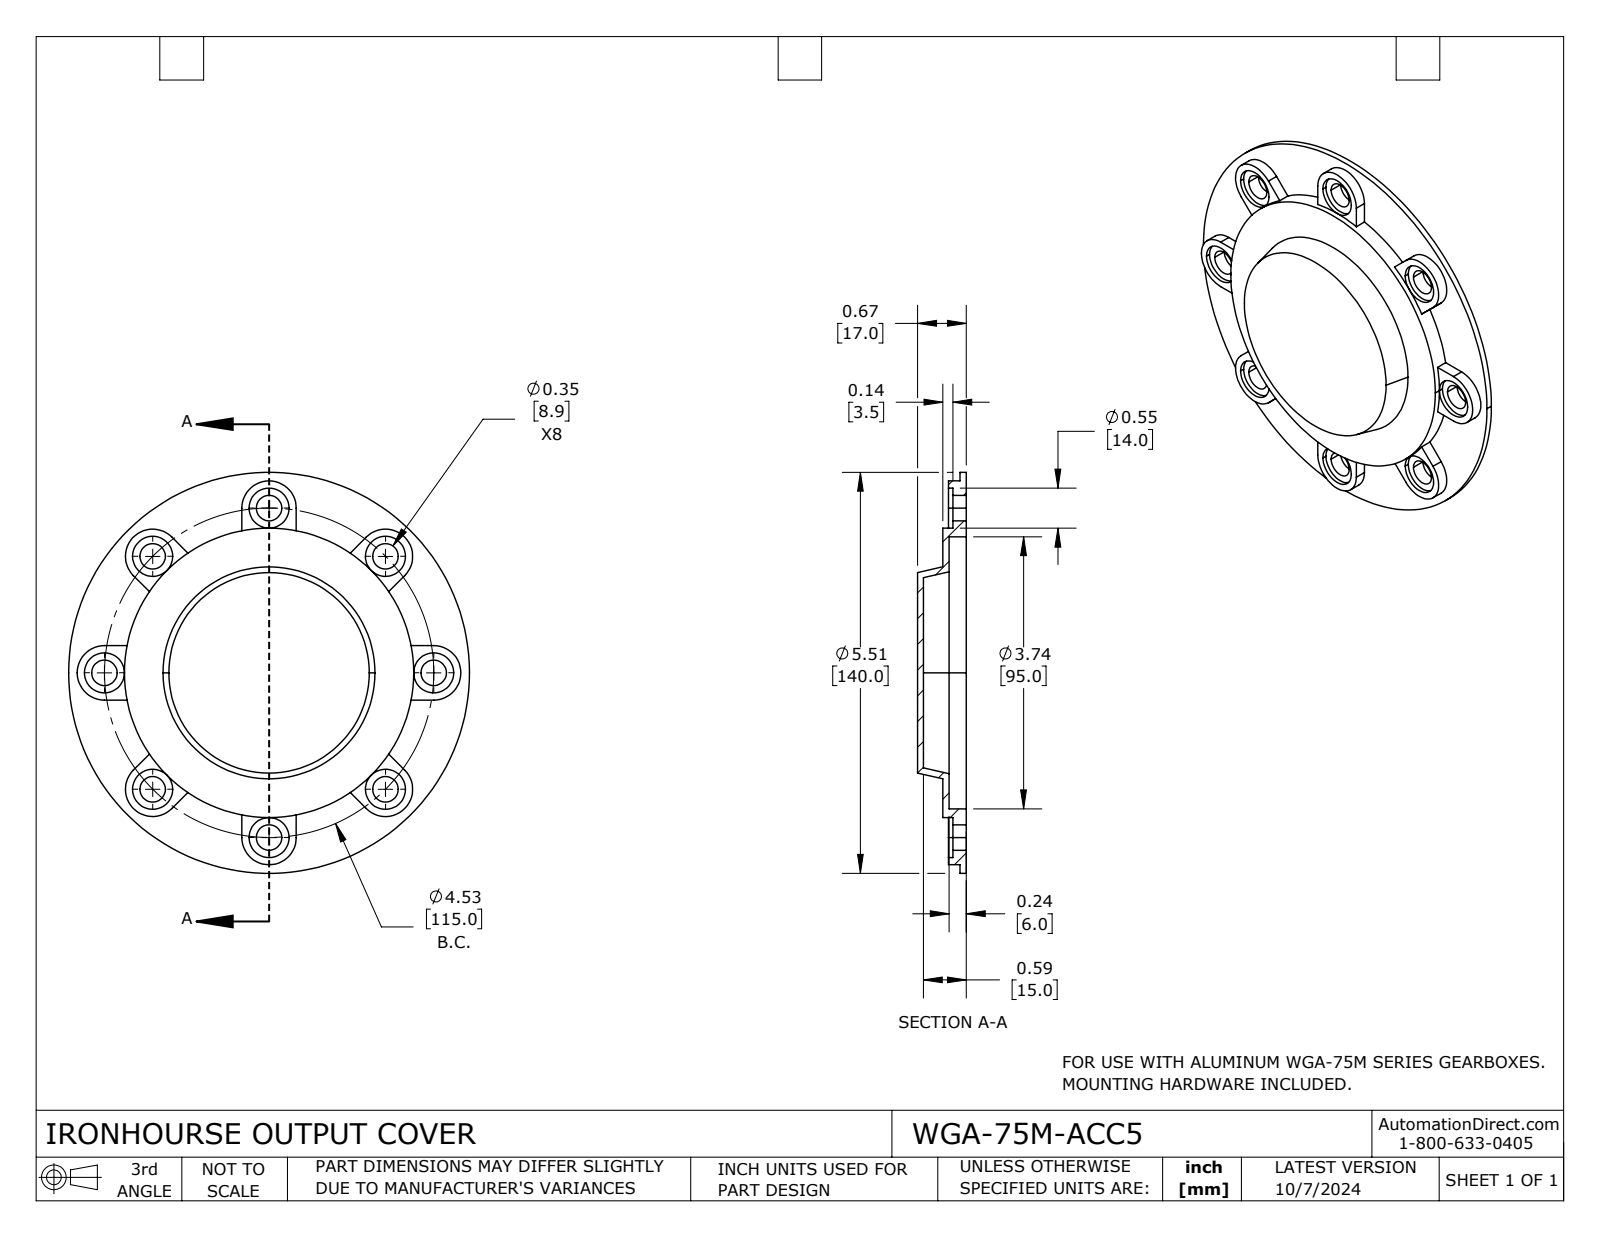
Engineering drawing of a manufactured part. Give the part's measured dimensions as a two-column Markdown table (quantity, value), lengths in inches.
| quantity | value |
| --- | --- |
| part name | WGA-75M-ACC5 |
| STEP written by | SolidWorks 2023 (CONFIG_CONTROL_DESIGN) |
| units | inches |
| bodies | 1 solid, 91 faces (38 planar, 49 cylindrical, 4 other) |
| overall size | 5.512 × 5.512 × 0.669 |
| volume | 2.863 in³ |
| surface area | 62.02 in² |
| round holes (diameter × count) | 0.35 × 8, 0.551 × 8, 3.74 × 1 |
| round bosses / shafts (diameter × count) | 5.512 × 1, 3.976 × 1 |
| partial cylindrical surfaces (radius × count) | 0.374 × 8 |
| main face-to-face distances | 0.087, 0.236, 0.346, 0.079, 0.583, 0.669, 0.323, 0.268, 0.504, 0.591 |
| hole center spacings | 1.733, 2.264, 3.202, 4.183, 4.528 |
